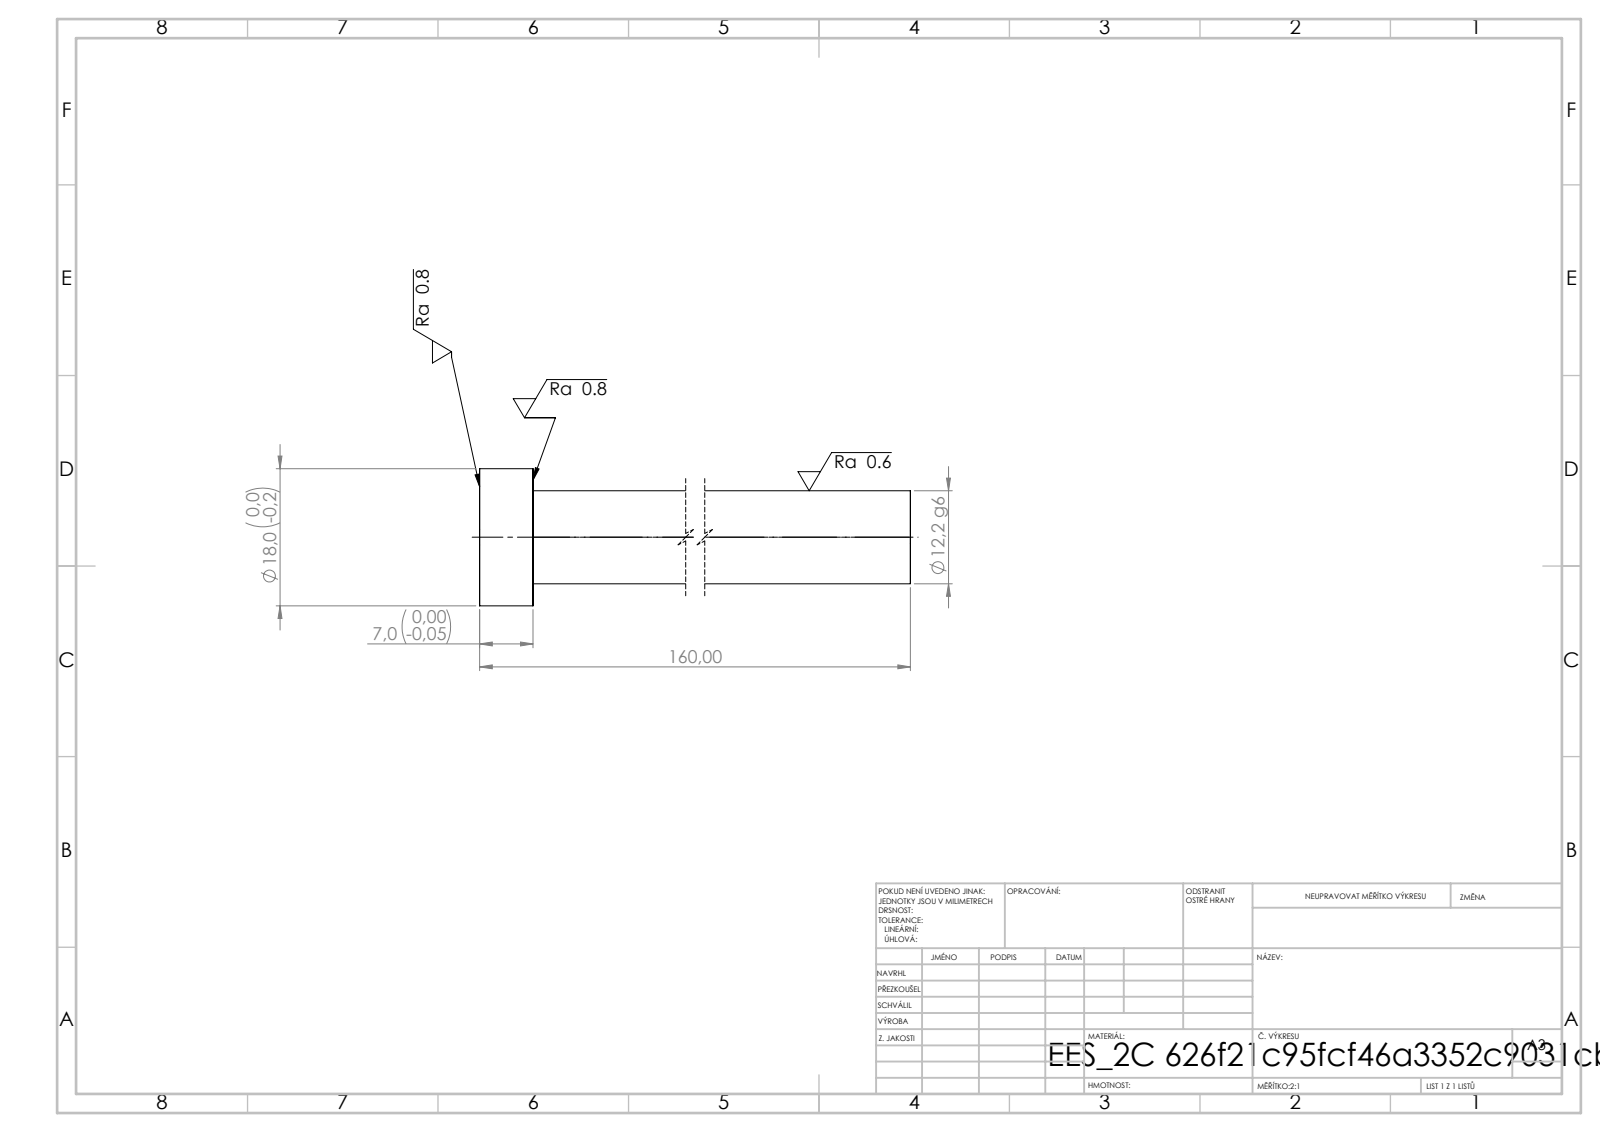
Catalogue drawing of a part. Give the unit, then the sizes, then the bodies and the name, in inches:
Units: inches
Overall size (bounding box): 6.299 × 0.709 × 0.709
Round bosses / shafts (diameter × count): ⌀0.709 ×1, ⌀0.48 ×1
Main face-to-face distances: 0.276, 6.299, 6.024
Volume: 1.2 in³ · Surface area: 10.49 in²
Bodies: 1 solid, 7 faces (3 planar, 4 cylindrical, 0 other)
STEP written by: SolidWorks 2019 (CONFIG_CONTROL_DESIGN)
